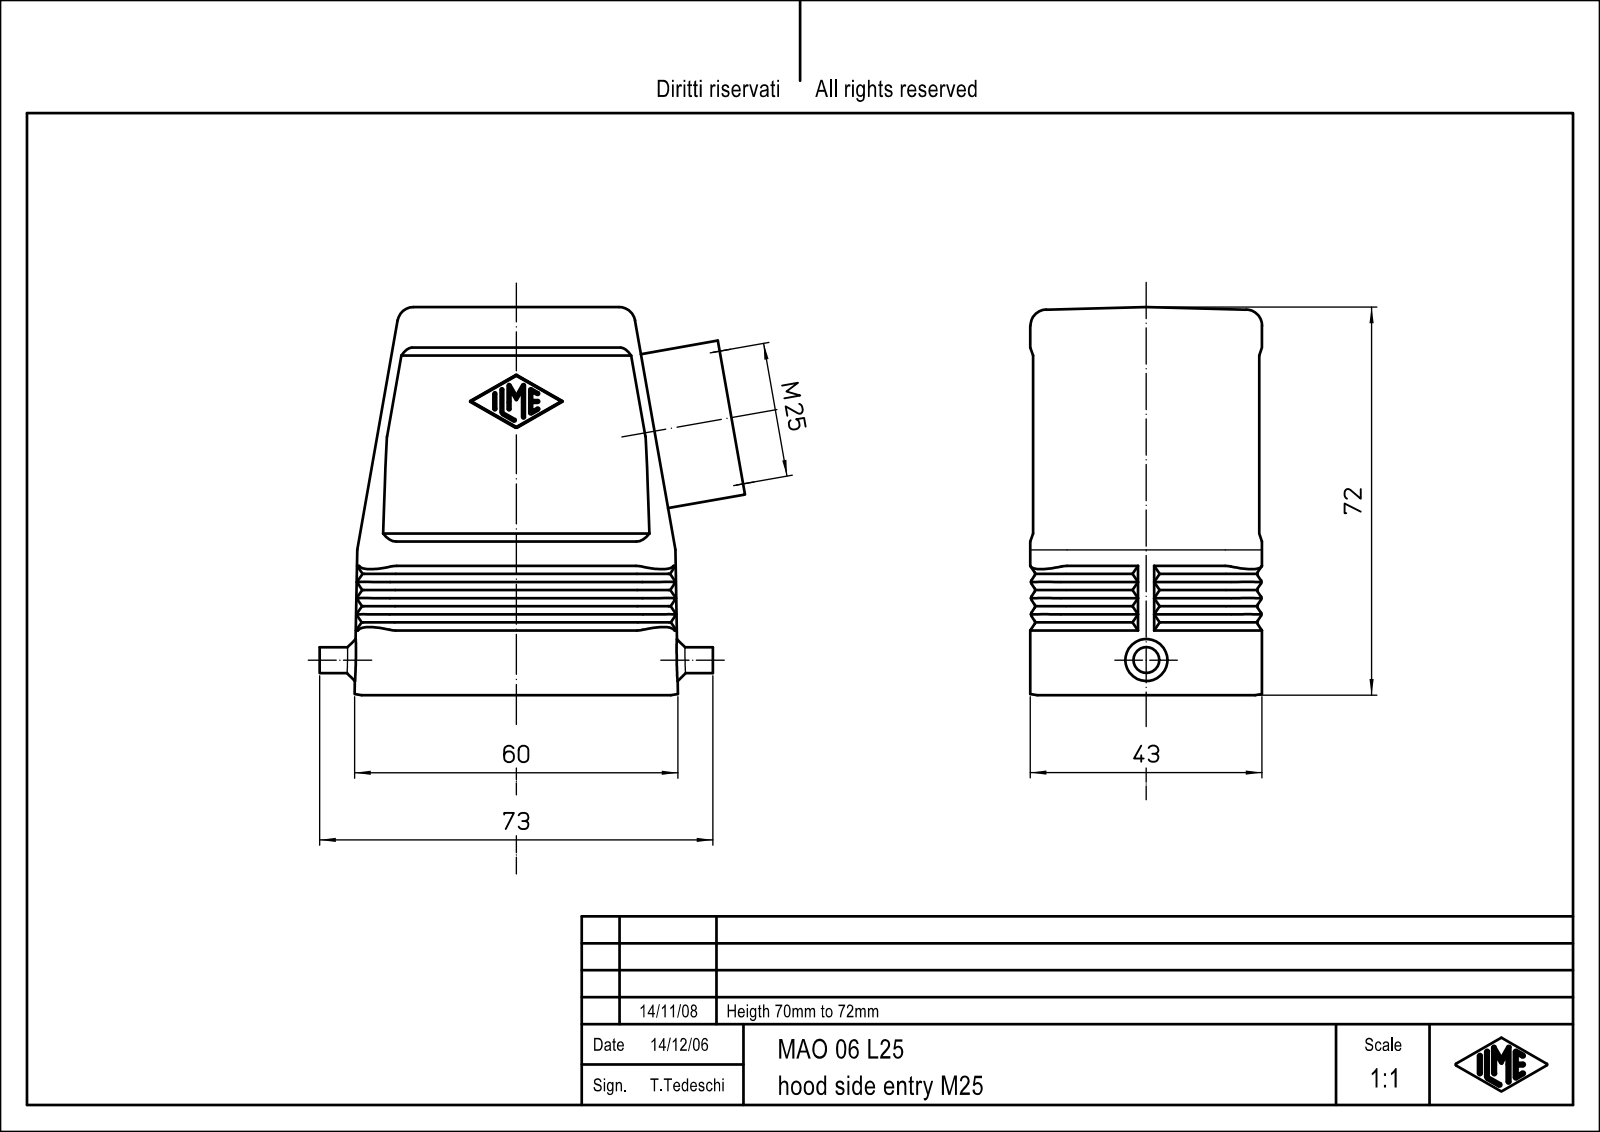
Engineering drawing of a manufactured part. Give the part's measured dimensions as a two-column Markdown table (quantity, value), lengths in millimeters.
| quantity | value |
| --- | --- |
| part name | MAO_06_L25 |
| STEP written by | CoCreate Modeling 16.00A 16-Aug-2008 (C) Parametric Technology GmbH (AUTOMOTIVE_DESIGN) |
| units | millimeters |
| bodies | 1 solid, 316 faces (168 planar, 105 cylindrical, 43 other) |
| overall size | 78.95 × 72 × 43 |
| volume | 59 157 mm³ |
| surface area | 30 852 mm² |
| round holes (diameter × count) | 3.5 × 4, 20 × 1, 25 × 1, 29.5 × 1 |
| round bosses / shafts (diameter × count) | 29 × 1, 4.8 × 1 |
| partial cylindrical surfaces (radius × count) | 7 × 36, 0.33 × 15, 3 × 14, 0.17 × 3, 0.5 × 1, 0.67 × 1, 1 × 1, 12.5 × 1 |
| main face-to-face distances | 0.5, 42.5, 42, 1.65, 7.95, 43, 1.66, 34.11, 3.33, 1.67 |
| hole center spacings | 27, 44, 51.62 |
